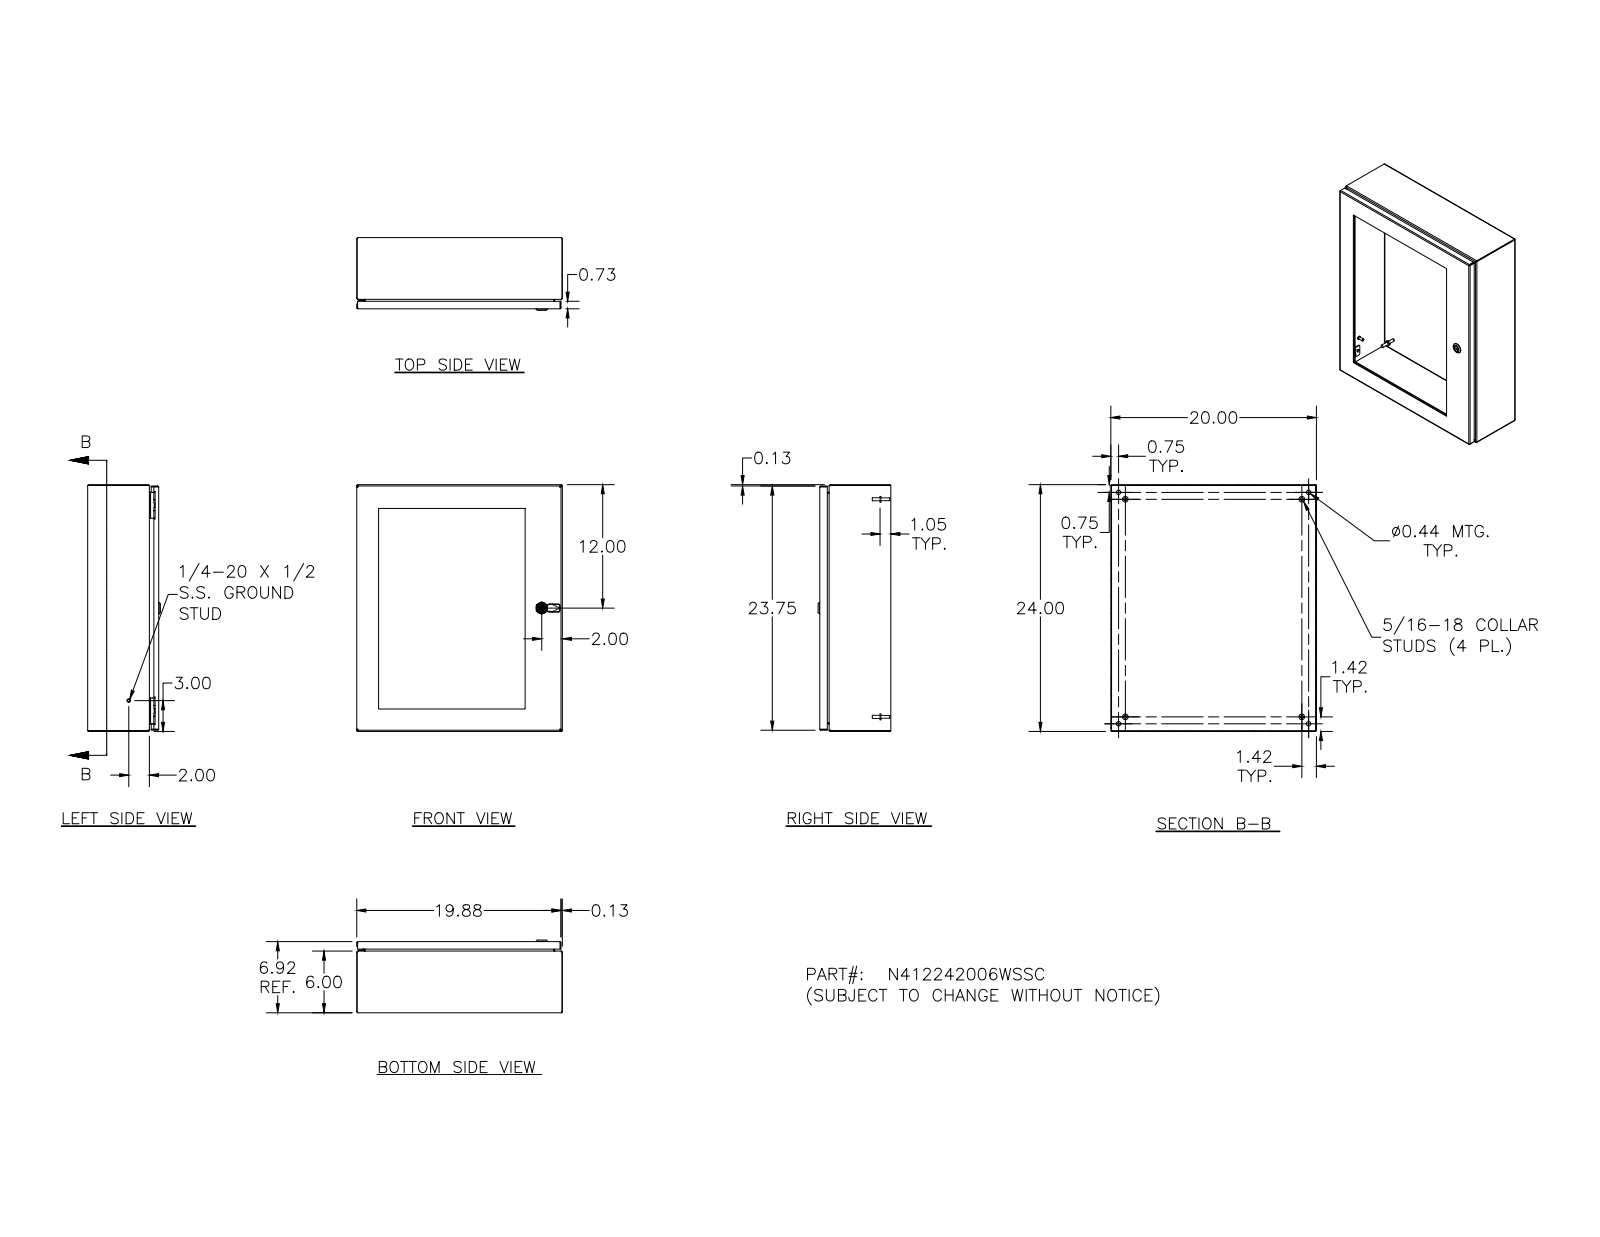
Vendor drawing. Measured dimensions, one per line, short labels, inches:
name: N412242006WSSC; N412242006WSSCBKP; N4122420WSSCLID; HFW328176 (+8 more)
written by: Autodesk Inventor 2011 (AUTOMOTIVE_DESIGN)
unit: in
bodies: 74 solids, 2004 faces (776 planar, 573 cylindrical, 655 other)
size: 24 × 20 × 7.075
volume: 186.9 in³; area: 3 620 in²
holes: 20× ⌀0.156, 18× ⌀0.281, 4× ⌀0.093, 4× ⌀0.152, 4× ⌀0.167, 4× ⌀0.172, 4× ⌀0.188, 4× ⌀0.437, 1× ⌀0.187, 1× ⌀0.197, 1× ⌀0.315, 1× ⌀0.394
bosses: 18× ⌀0.19, 17× ⌀0.253, 10× ⌀0.25, 4× ⌀0.563, 4× ⌀0.36, 4× ⌀0.32, 4× ⌀0.3, 4× ⌀0.275
rounds: 34× R0.031, 26× R0.05, 24× R0.105, 18× R0.016, 16× R0.125, 9× R0.02, 8× R0.032, 4× R0.157
face distances: 0.074, 6.843, 6.769, 0.25, 6.593, 6.519, 19.926, 23.926, 6.917, 0.324
hole spacings: 4, 8, 16.008, 12, 17.443, 20, 21.132, 15.5
